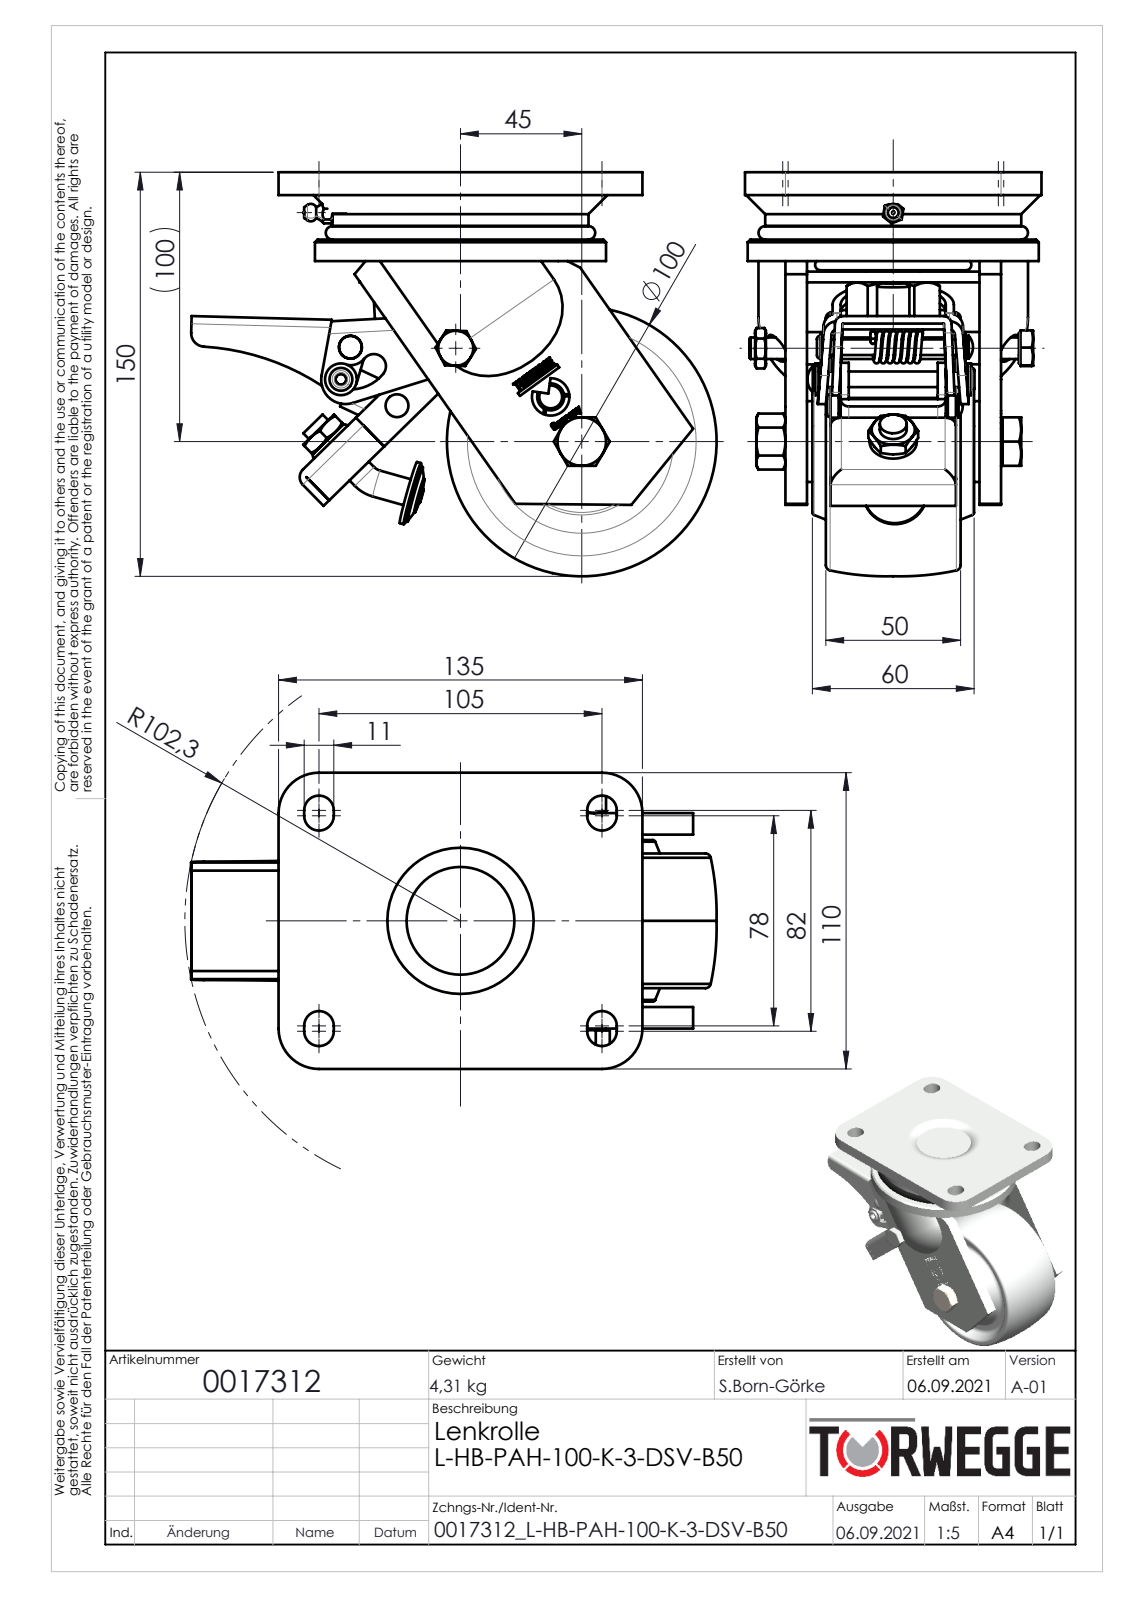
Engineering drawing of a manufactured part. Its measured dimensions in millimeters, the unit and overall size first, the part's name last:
Units: millimetres
Overall size (bounding box): 194.95 × 150.03 × 110
Round holes (diameter × count): ⌀6 ×4, ⌀4 ×3, ⌀8.4 ×2, ⌀8.5 ×2, ⌀10 ×2, ⌀5.8 ×1, ⌀6.3 ×1, ⌀6.8 ×1, ⌀8 ×1, ⌀8.2 ×1, ⌀8.38 ×1, ⌀10.2 ×1
Round bosses / shafts (diameter × count): ⌀12 ×3, ⌀8.5 ×3, ⌀5.8 ×2, ⌀2 ×2, ⌀108 ×1, ⌀75 ×1, ⌀30 ×1, ⌀27.17 ×1
Partial cylindrical surfaces — rounded edges, fillets, slot ends (radius × count): R5.5 ×8, R4 ×5, R8 ×5, R3 ×4, R5 ×4, R15 ×4, R0.2 ×2, R1 ×2
Main face-to-face distances: 8, 2, 10, 25, 72, 8.5, 16.5, 23, 3, 24.5
Hole centre spacings: 1.48, 12.42, 20.2, 23.01, 27.76, 29.49, 30.5, 37.6
Volume: 871 762 mm³ · Surface area: 243 559 mm²
Bodies: 45 solids, 1300 faces (532 planar, 303 cylindrical, 465 other)
Part name (STEP PRODUCT): 0017312
STEP written by: SolidWorks 2020 (AUTOMOTIVE_DESIGN)
